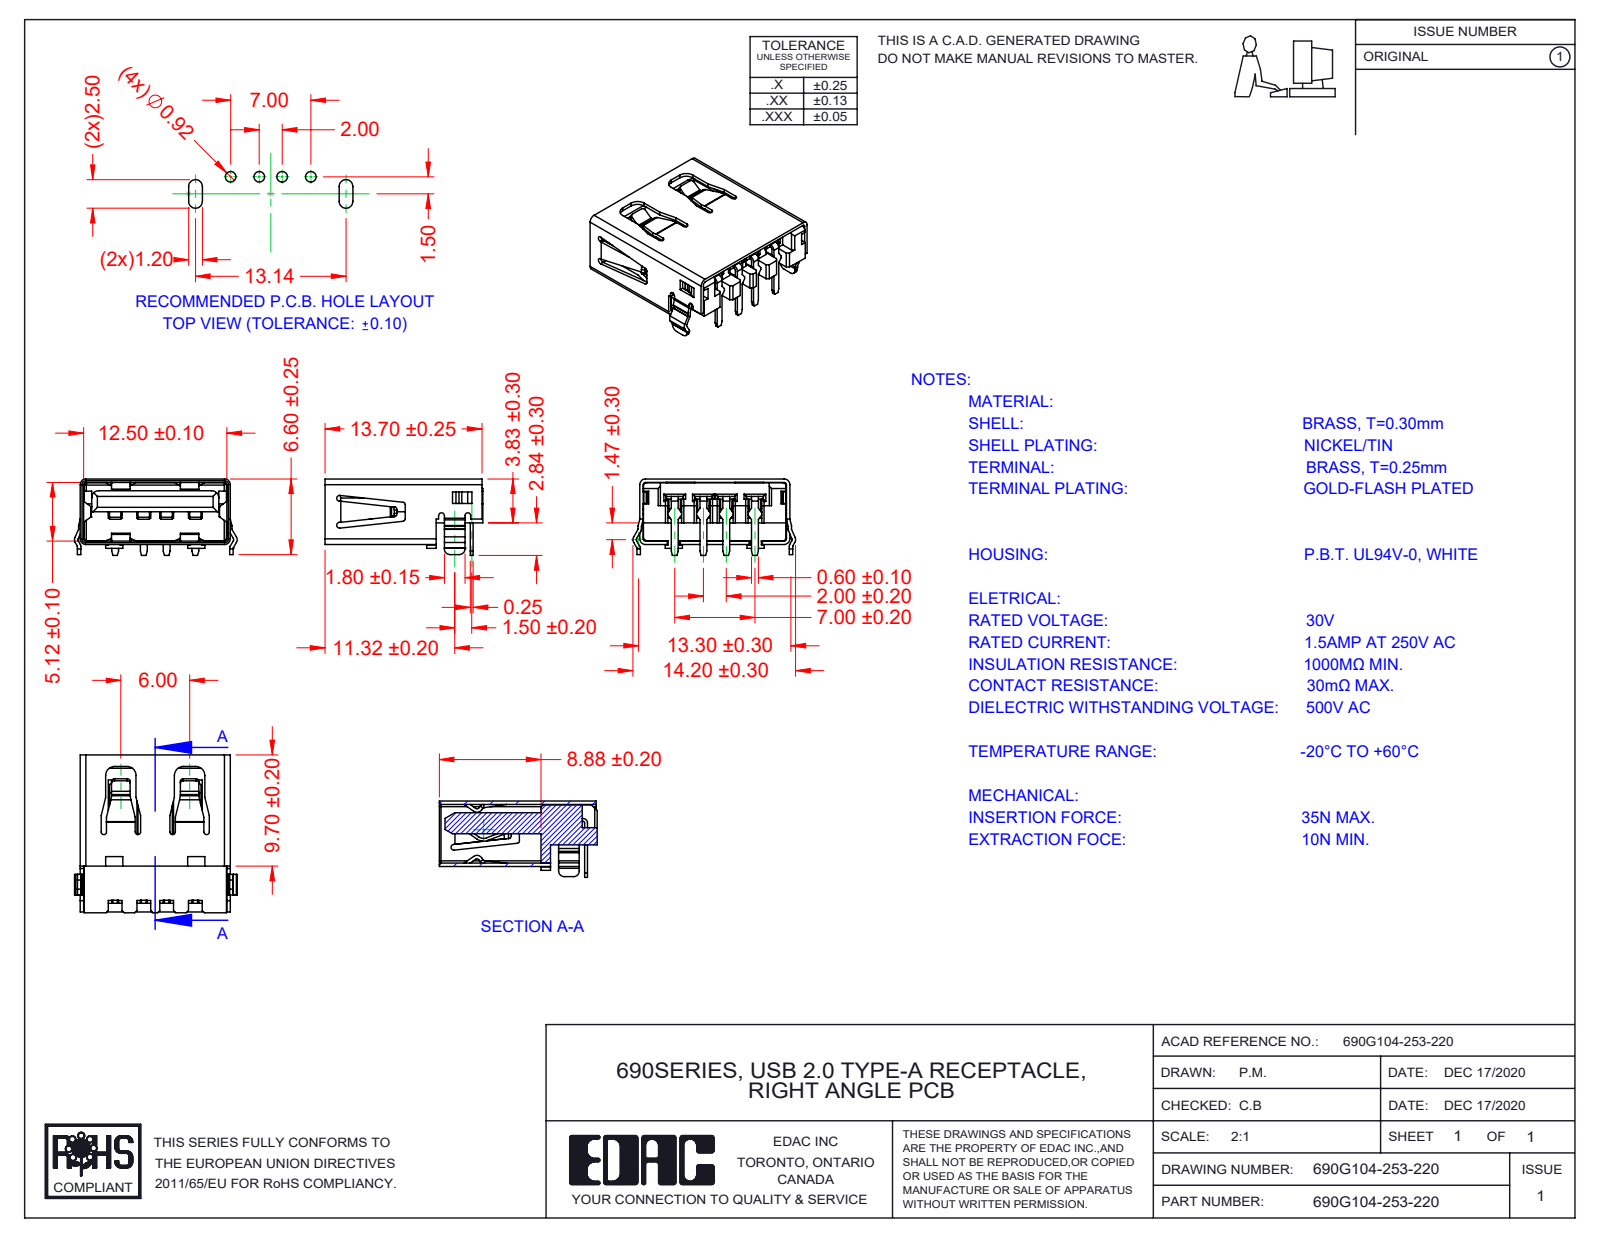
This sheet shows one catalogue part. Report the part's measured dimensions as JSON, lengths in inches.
{"part_name": "690G104-253-220; Contact 690G104-253-22X; Shell 690G104-253-22X; Insulator 690G104-253-22X_White", "step_written_by": "SolidWorks 2020 (AUTOMOTIVE_DESIGN)", "units": "inches", "bodies": {"solids": 6, "faces": 738, "planar": 554, "cylindrical": 164, "other": 20}, "overall_size": [0.559, 0.543, 0.263], "volume_in3": 0.025, "surface_area_in2": 2.654, "partial_cylinders_radius": [[0.01, 22], [0.008, 14], [0.02, 14], [0.004, 10], [0.024, 6], [0.012, 5], [0.035, 5], [0.031, 4]], "face_to_face_distances": [0.213, 0.101, 0.113, 0.225, 0.202, 0.504, 0.048, 0.02, 0.06, 0.165]}
